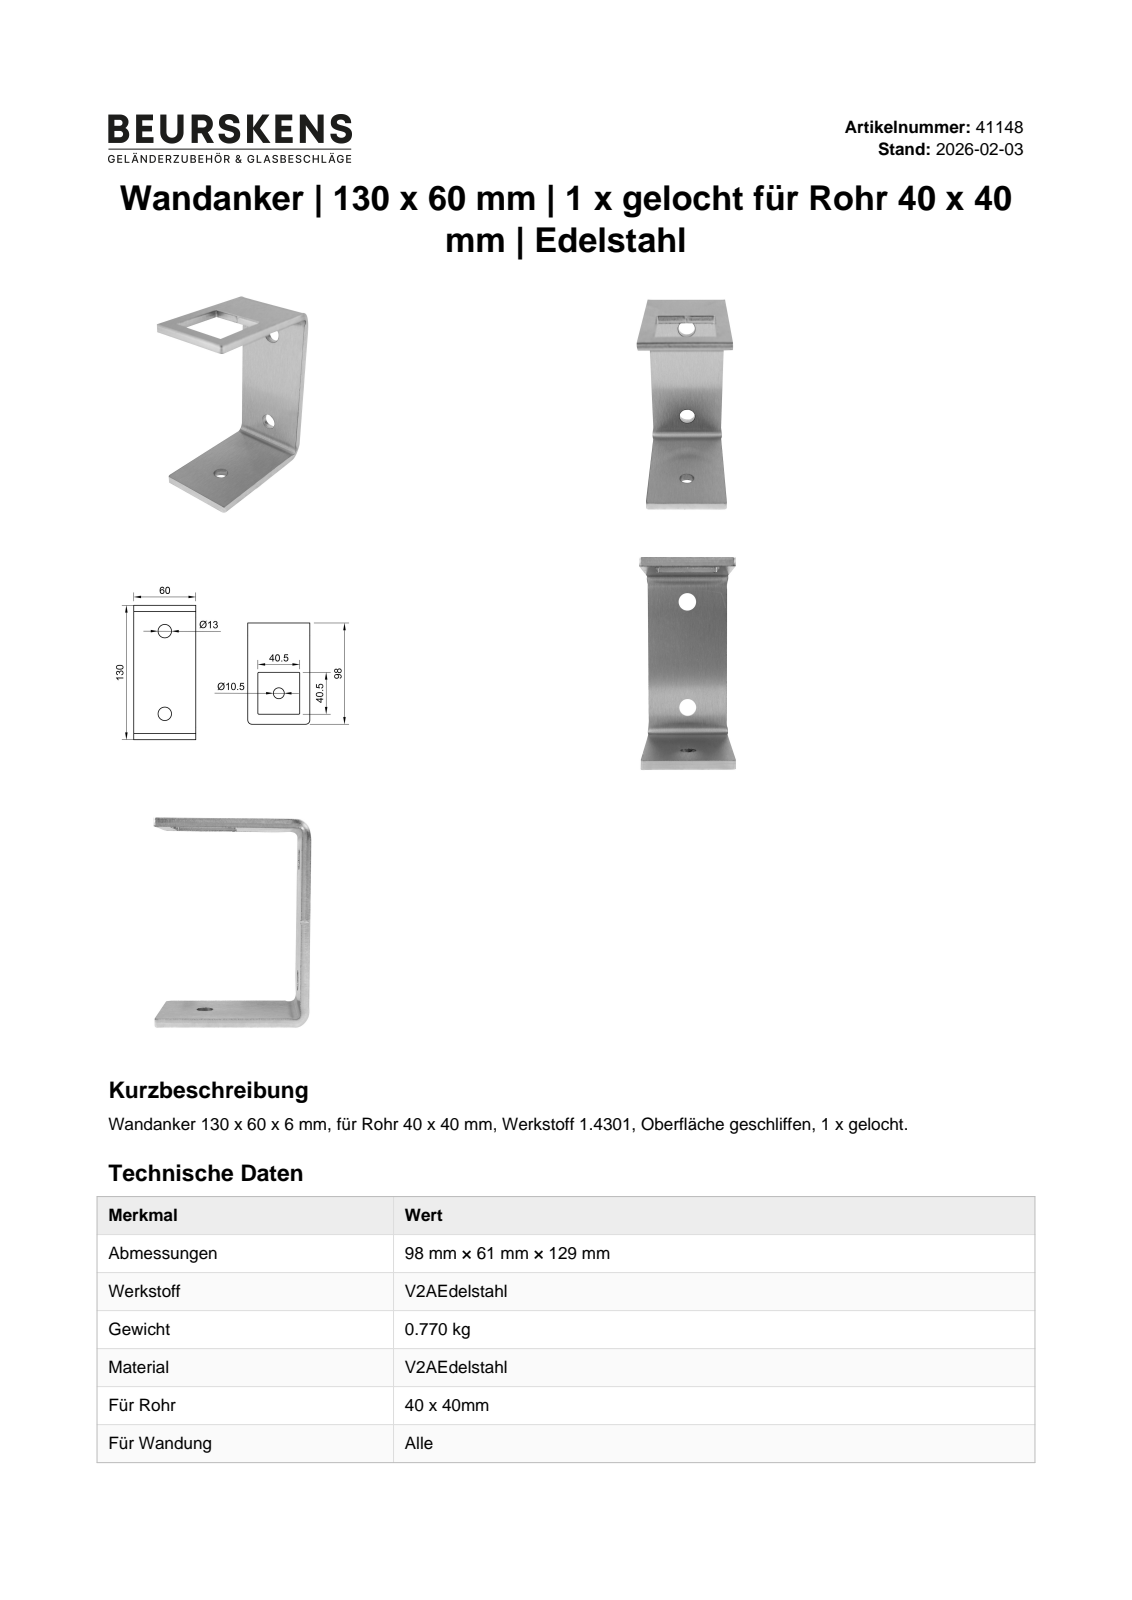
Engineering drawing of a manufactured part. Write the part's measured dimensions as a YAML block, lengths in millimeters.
part_name: "41148"
step_written_by: "Autodesk Inventor 2022 (AUTOMOTIVE_DESIGN)"
units: millimeters
bodies: {solids: 1, faces: 37, planar: 22, cylindrical: 15, other: 0}
overall_size: [130, 98, 60]
volume: 98228
surface_area: 38746
round_holes:
  - {diameter: 13, count: 2}
  - {diameter: 10.5, count: 1}
partial_cylinders:
  - {radius: 1, count: 4}
  - {radius: 4, count: 2}
  - {radius: 6, count: 2}
  - {radius: 12, count: 2}
face_to_face_distances: [6, 124, 118, 130, 60, 9.75, 50.25, 98, 92, 40.5]
hole_center_spacings: [80]
